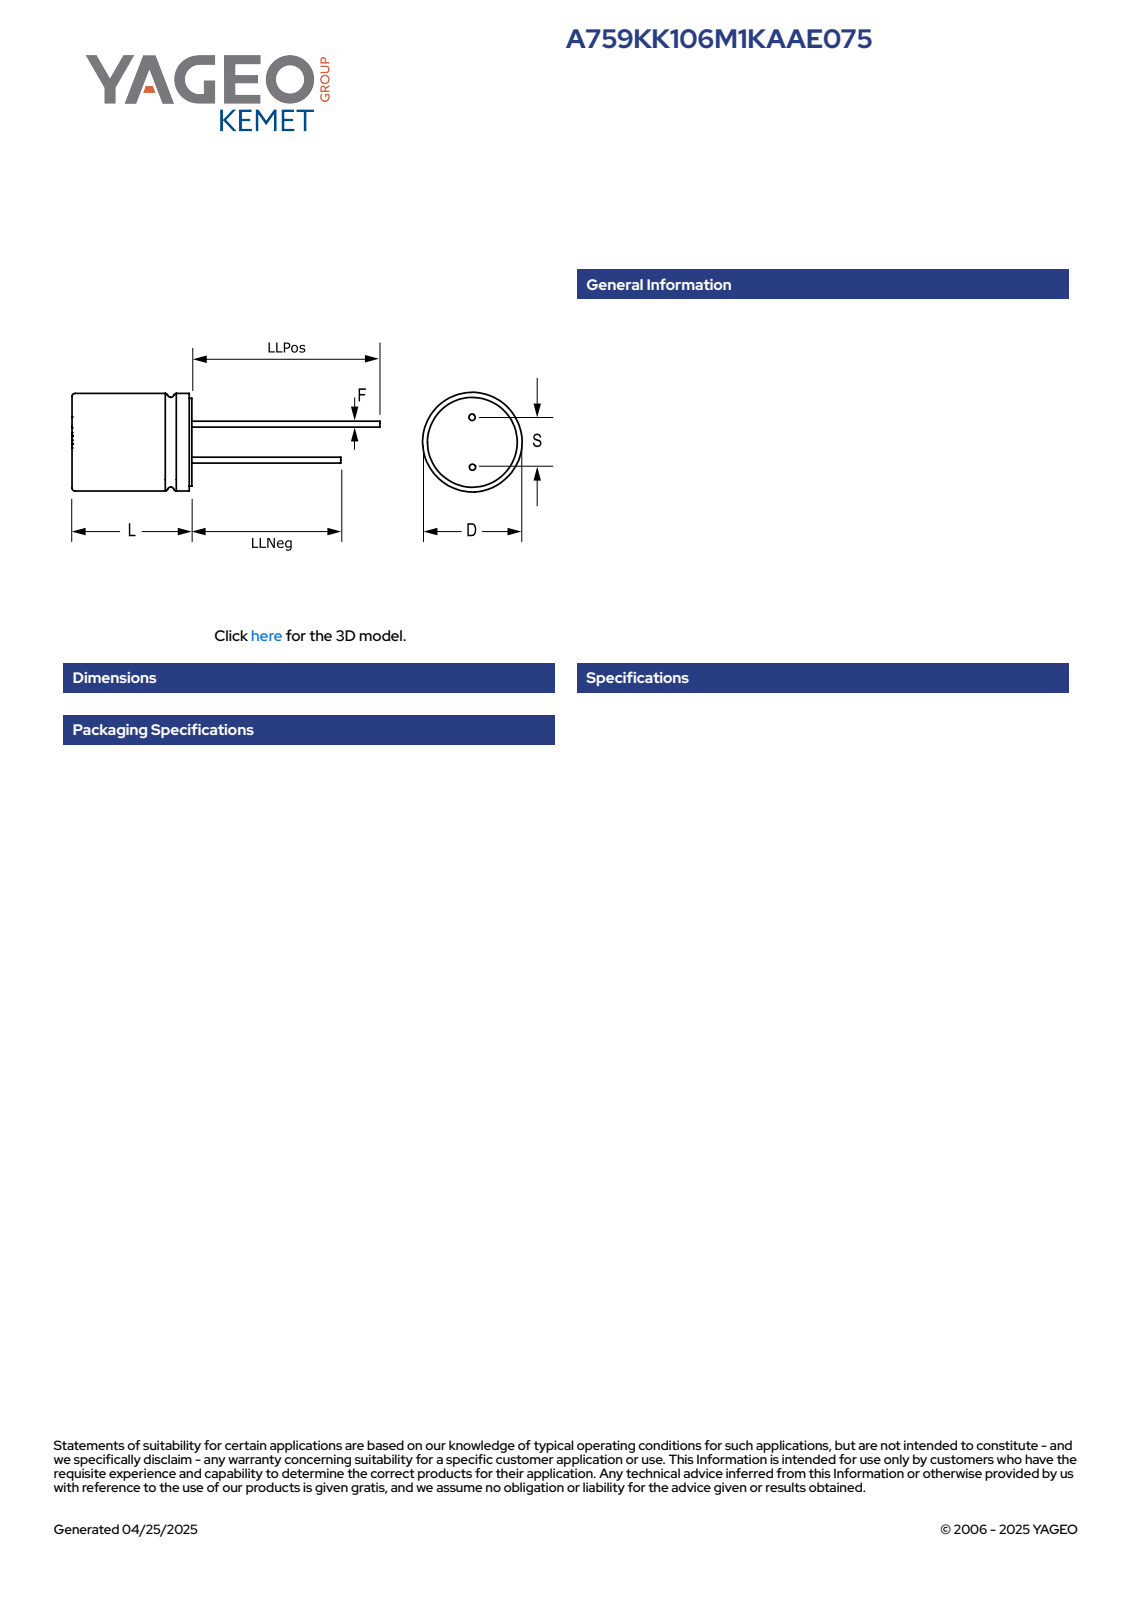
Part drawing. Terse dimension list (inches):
name: CAR_KP_8X8_D8.5L9S3.5F0.65
written by: SolidWorks 2014 (AUTOMOTIVE_DESIGN)
unit: in
bodies: 4 solids, 75 faces (61 planar, 8 cylindrical, 6 other)
size: 1.102 × 0.335 × 0.335
volume: 0.032 in³; area: 0.673 in²
bosses: 2× ⌀0.026, 1× ⌀0.335
face distances: 0.354, 0.355, 0.945, 1.103, 0.945, 1.102, 0.591, 0.748, 0.157, 0.037
